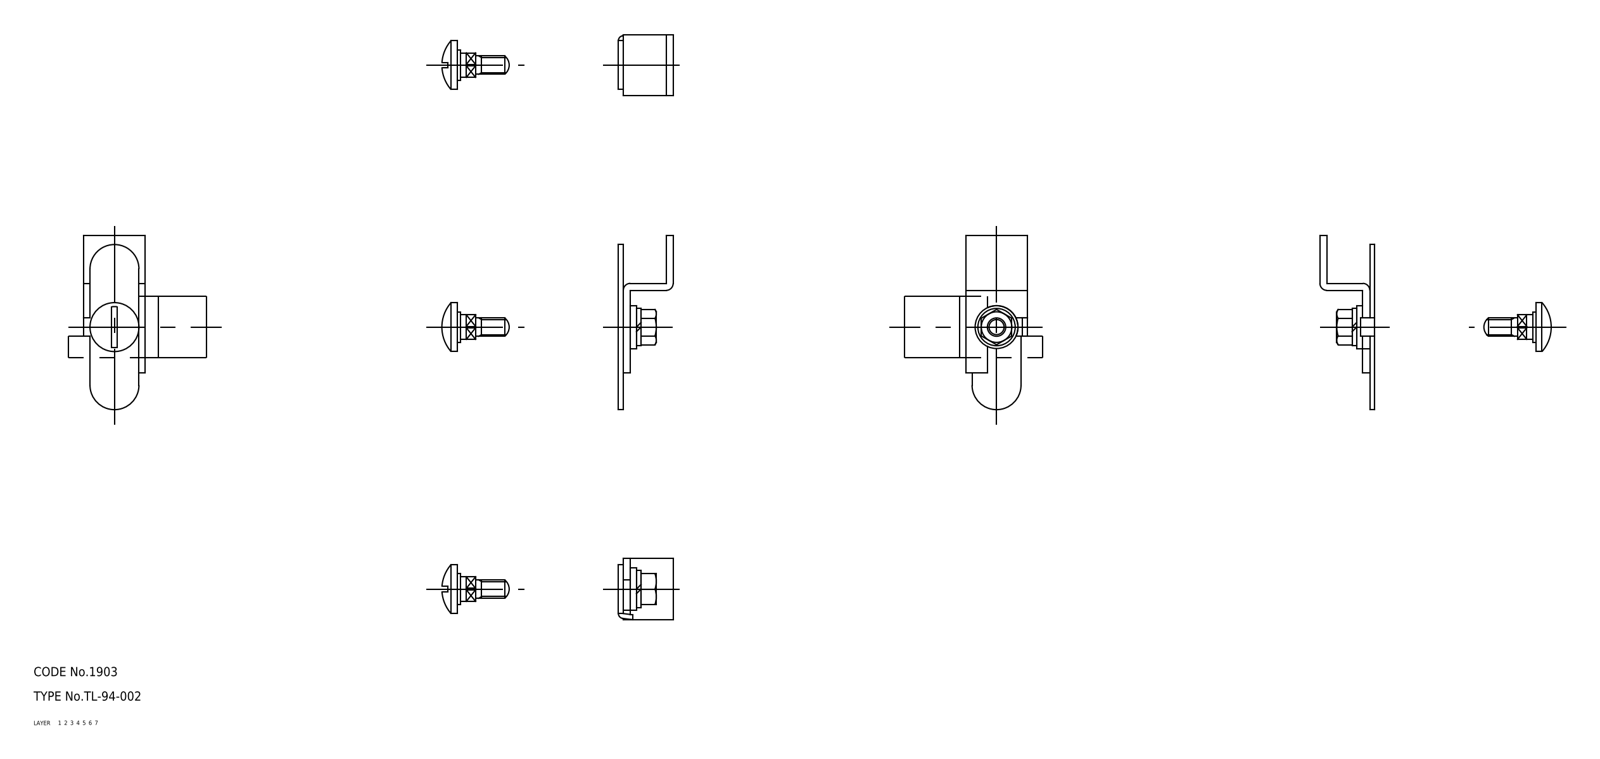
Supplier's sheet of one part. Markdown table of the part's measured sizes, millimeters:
| quantity | value |
| --- | --- |
| part name | washer; nut; knob; cam (+2 more) |
| STEP written by | CADfix (AUTOMOTIVE_DESIGN) |
| units | millimeters |
| bodies | 5 solids, 89 faces (0 planar, 0 cylindrical, 89 other) |
| overall size | 57 × 24.97 × 20 |
| volume | 5 416 mm³ |
| surface area | 6 000 mm² |
